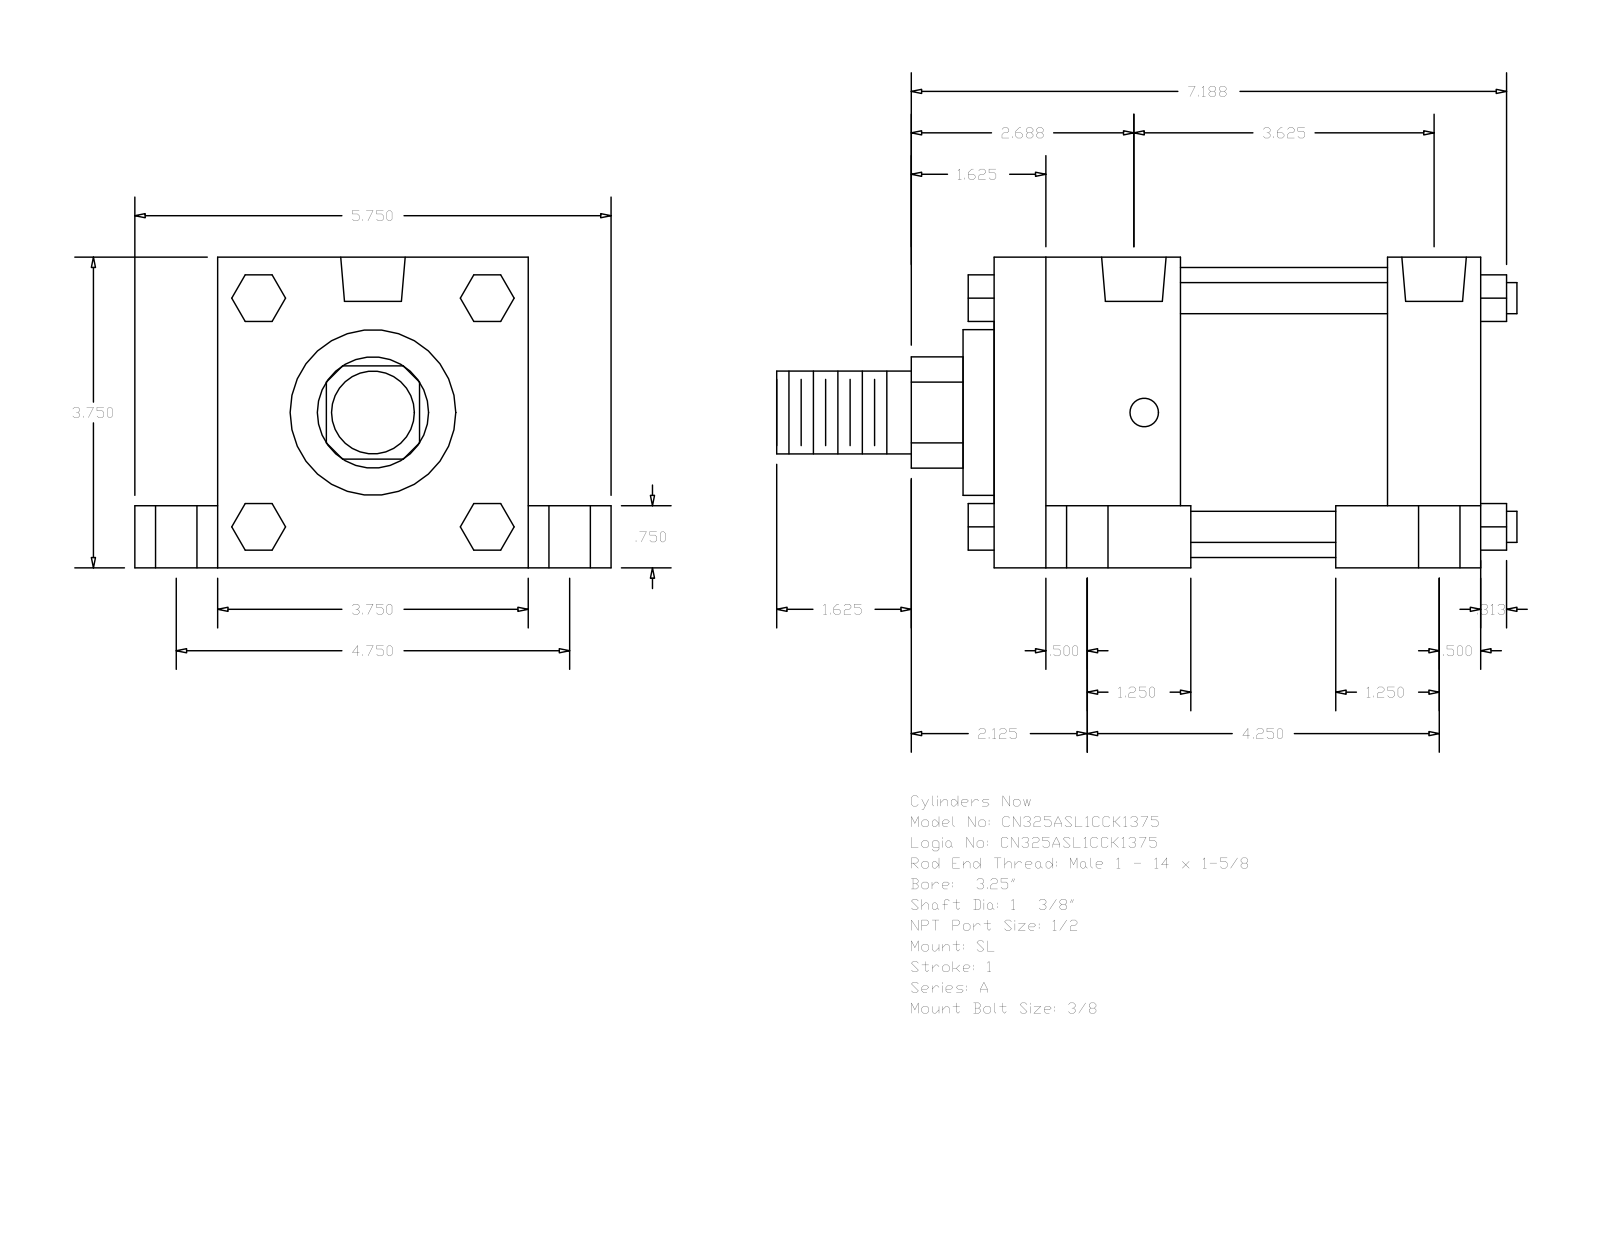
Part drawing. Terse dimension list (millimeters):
name: A_SL__0325_1.375
written by: GSSL Pune (CONFIG_CONTROL_DESIGN)
unit: mm
bodies: 0 solids, 150 faces (114 planar, 36 cylindrical, 0 other)
size: 227.01 × 146.05 × 95.25
holes: 4× ⌀8.73, 4× ⌀12.7, 4× ⌀19.05, 2× ⌀19.77
bosses: 4× ⌀9.53, 1× ⌀88.9, 1× ⌀50.8, 1× ⌀34.92, 1× ⌀25.4
rounds: 1× R17.06
face distances: 95.24, 149.22, 120.65, 25.41, 19.05, 76.19, 57.15, 28.57, 63.5, 92.07
hole spacings: 3.18, 60.35, 60.52, 62, 62.81, 85.72, 88.9, 107.95
